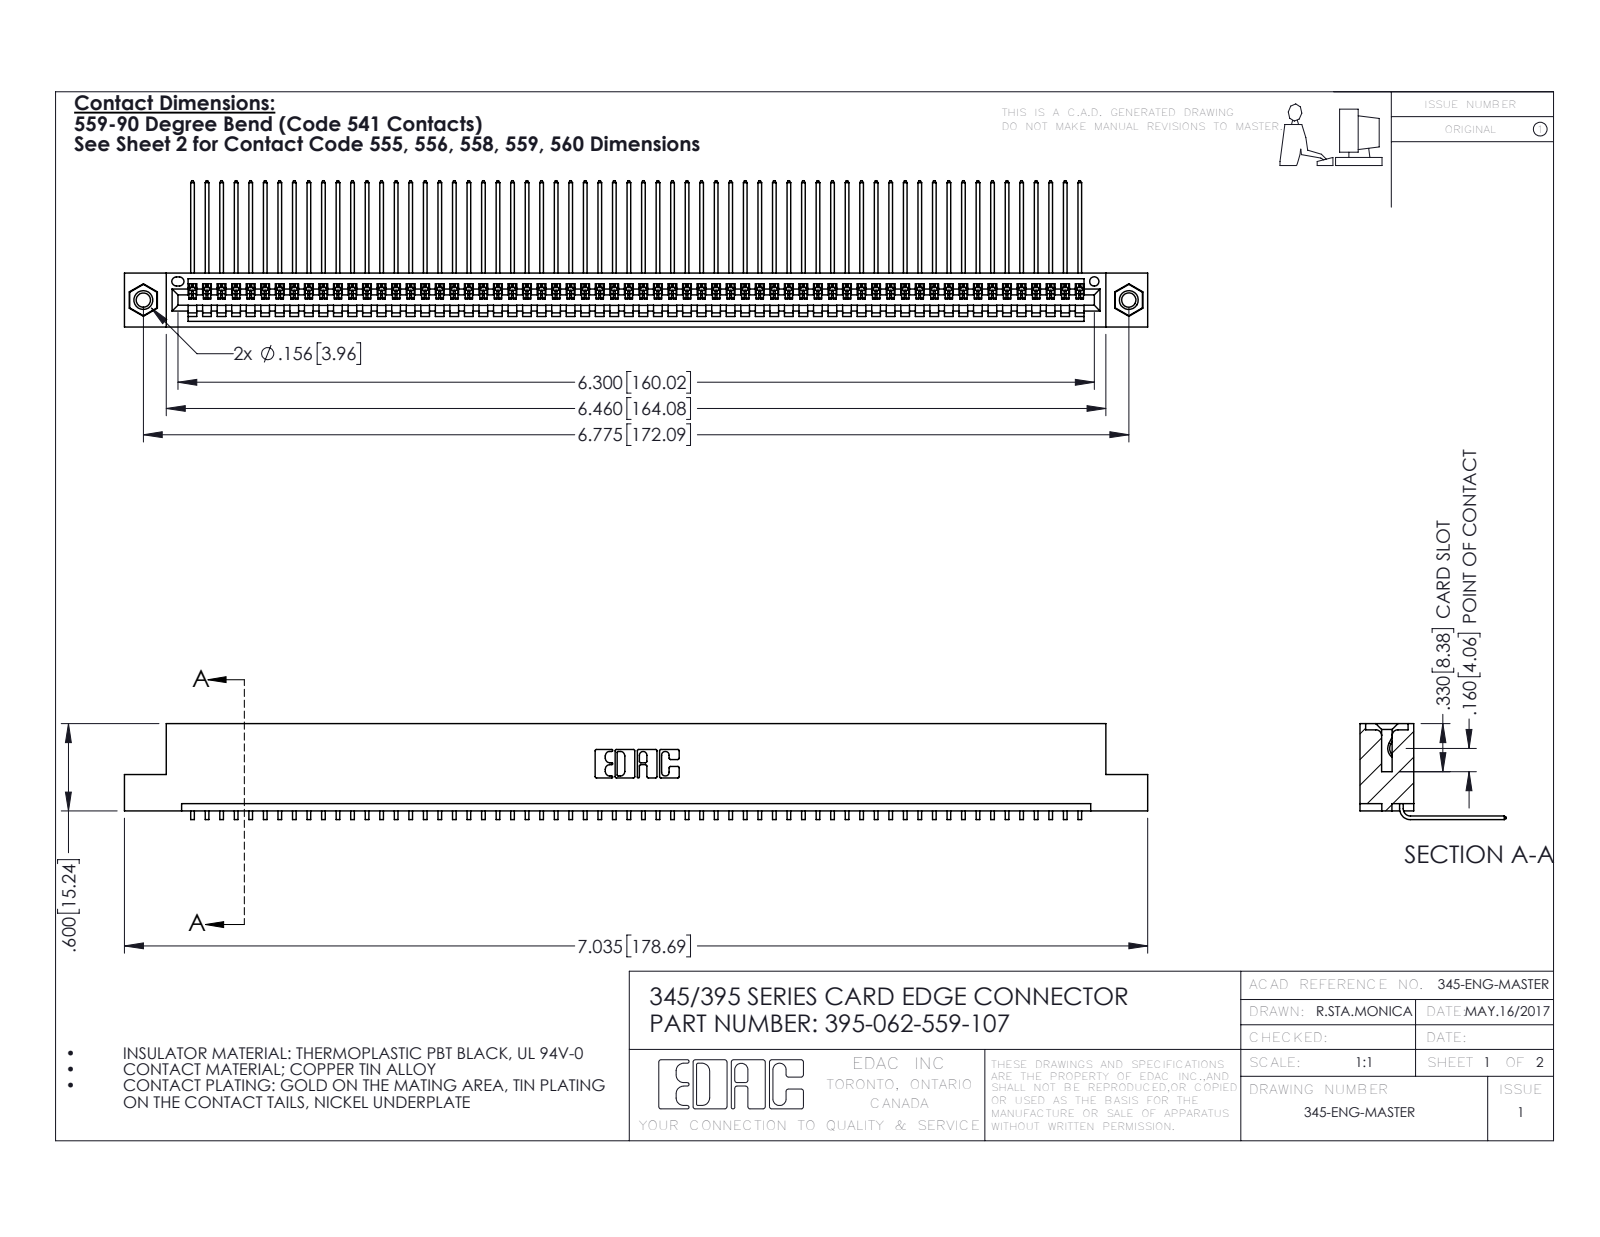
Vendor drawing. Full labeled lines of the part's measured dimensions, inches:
Part name (STEP PRODUCT): 345-250-001_345-250-005-103; 345 Part_Flush Mounting Lugs - 0.156 Dia-TI; 395-062-559-107; 345-292-001_558 559 Tail - 1
STEP written by: SolidWorks 2016 (CONFIG_CONTROL_DESIGN)
Units: inches
Bodies: 65 solids, 3906 faces (2716 planar, 1174 cylindrical, 16 other)
Overall size (bounding box): 7.035 × 1.005 × 0.659
Volume: 1.057 in³ · Surface area: 38.05 in²
Round holes (diameter × count): ⌀0.098 ×2, ⌀0.125 ×2, ⌀0.156 ×2, ⌀0.064 ×1
Round bosses / shafts (diameter × count): ⌀0.155 ×2
Partial cylindrical surfaces — rounded edges, fillets, slot ends (radius × count): R0.006 ×124, R0.01 ×22, R0.007 ×6, R0.031 ×6, R0.026 ×3, R0.031 ×2, R0.04 ×2, R0.014 ×1
Main face-to-face distances: 0.072, 0.298, 0.37, 0.2, 0.098, 0.272, 0.025, 0.225, 0.149, 0.072
Hole centre spacings: 0.27, 6.539, 6.775
